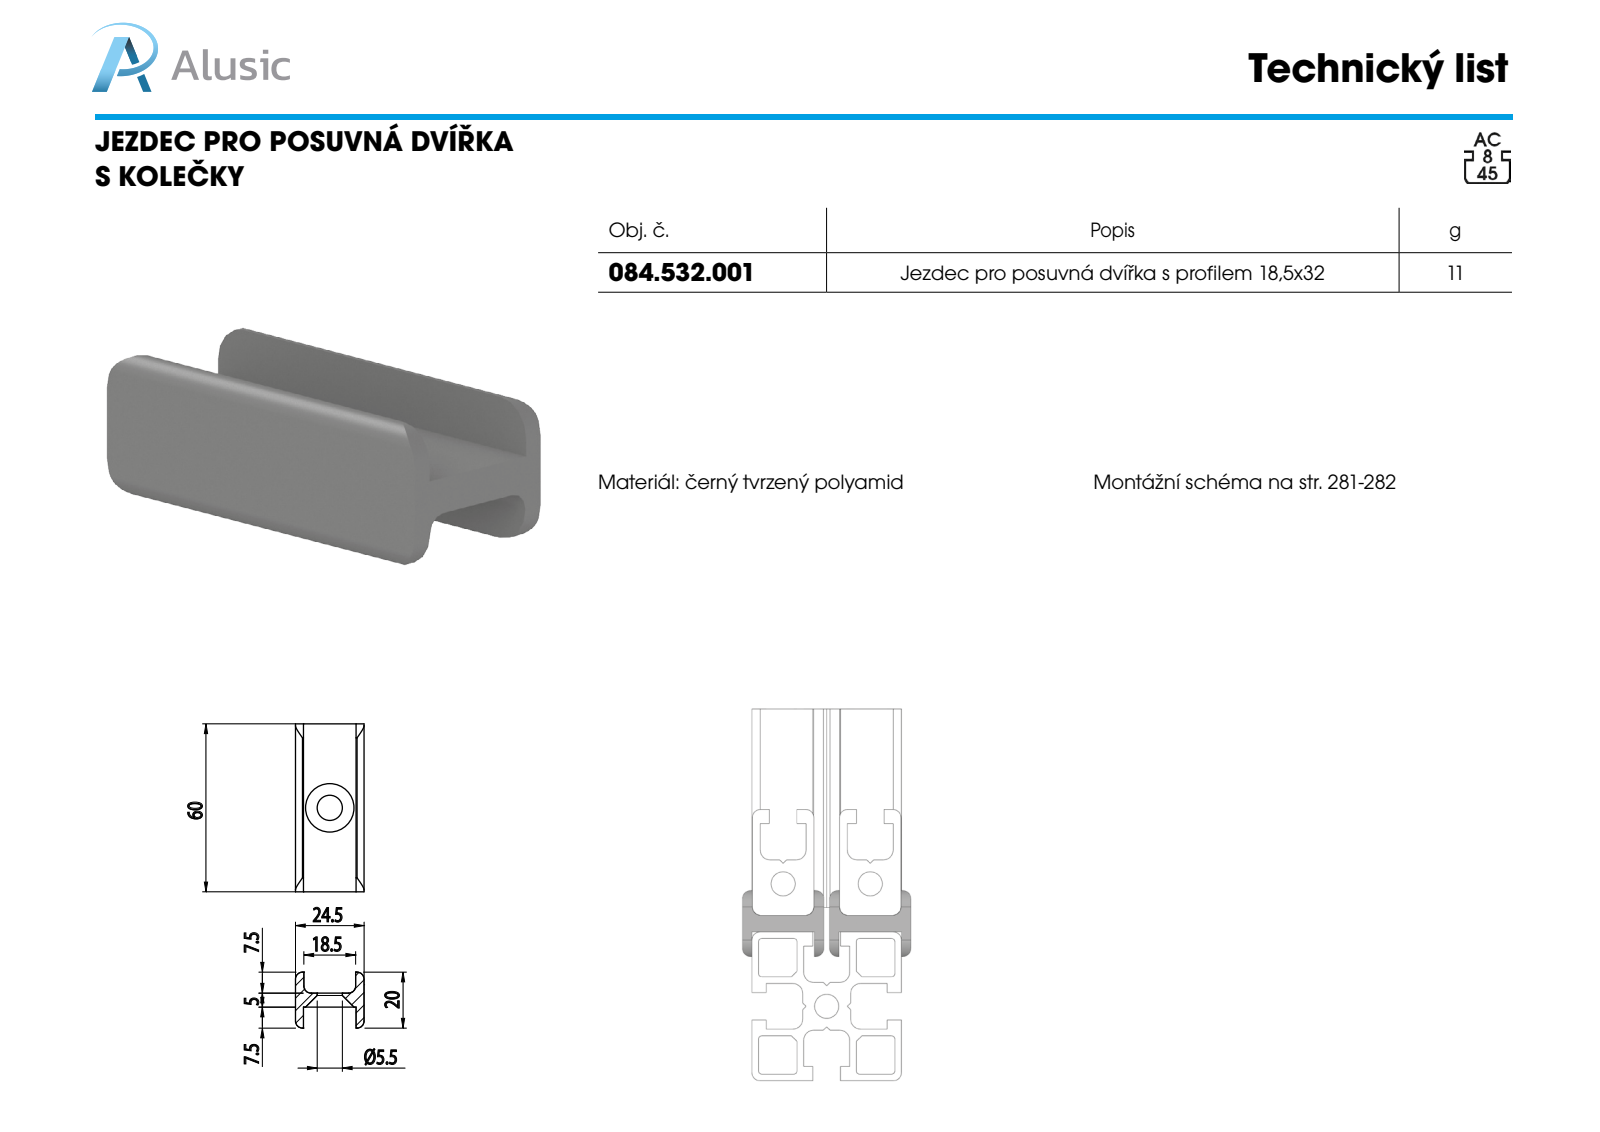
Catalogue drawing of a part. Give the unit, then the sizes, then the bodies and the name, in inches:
Units: inches
Overall size (bounding box): 2.362 × 0.965 × 0.787
Round holes (diameter × count): ⌀0.217 ×1
Partial cylindrical surfaces — rounded edges, fillets, slot ends (radius × count): R0.098 ×6
Main face-to-face distances: 0.118, 0.846, 0.965, 0.197, 0.728, 2.362, 0.295, 0.492, 0.787
Volume: 0.757 in³ · Surface area: 11.15 in²
Bodies: 1 solid, 24 faces (14 planar, 8 cylindrical, 2 other)
Part name (STEP PRODUCT): 084.532.001
STEP written by: SolidWorks 2011 (CONFIG_CONTROL_DESIGN)
